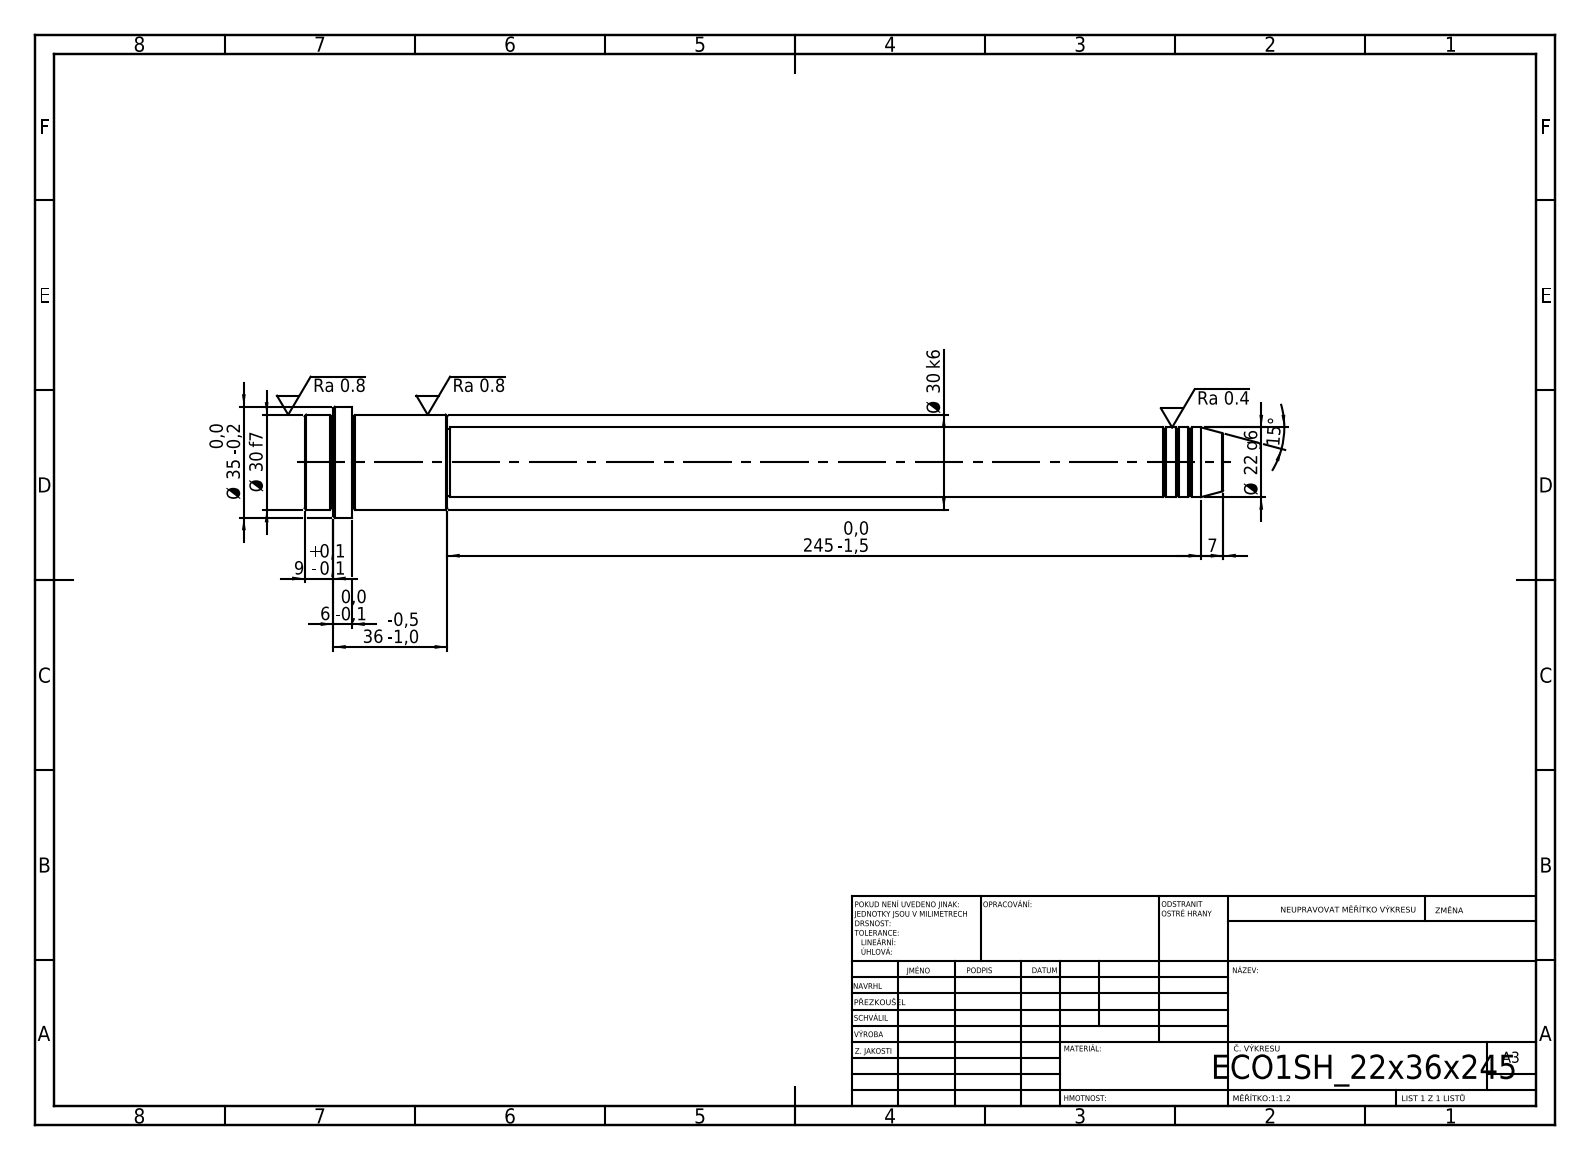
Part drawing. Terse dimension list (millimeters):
written by: SolidWorks 2019 (CONFIG_CONTROL_DESIGN)
unit: mm
bodies: 1 solid, 52 faces (6 planar, 16 cylindrical, 30 other)
size: 290 × 35 × 35
volume: 125 820 mm³; area: 23 228 mm²
bosses: 1× ⌀35, 1× ⌀30, 1× ⌀22, 1× ⌀21
face distances: 45, 30, 15, 245, 275, 290, 281, 36, 6, 9
